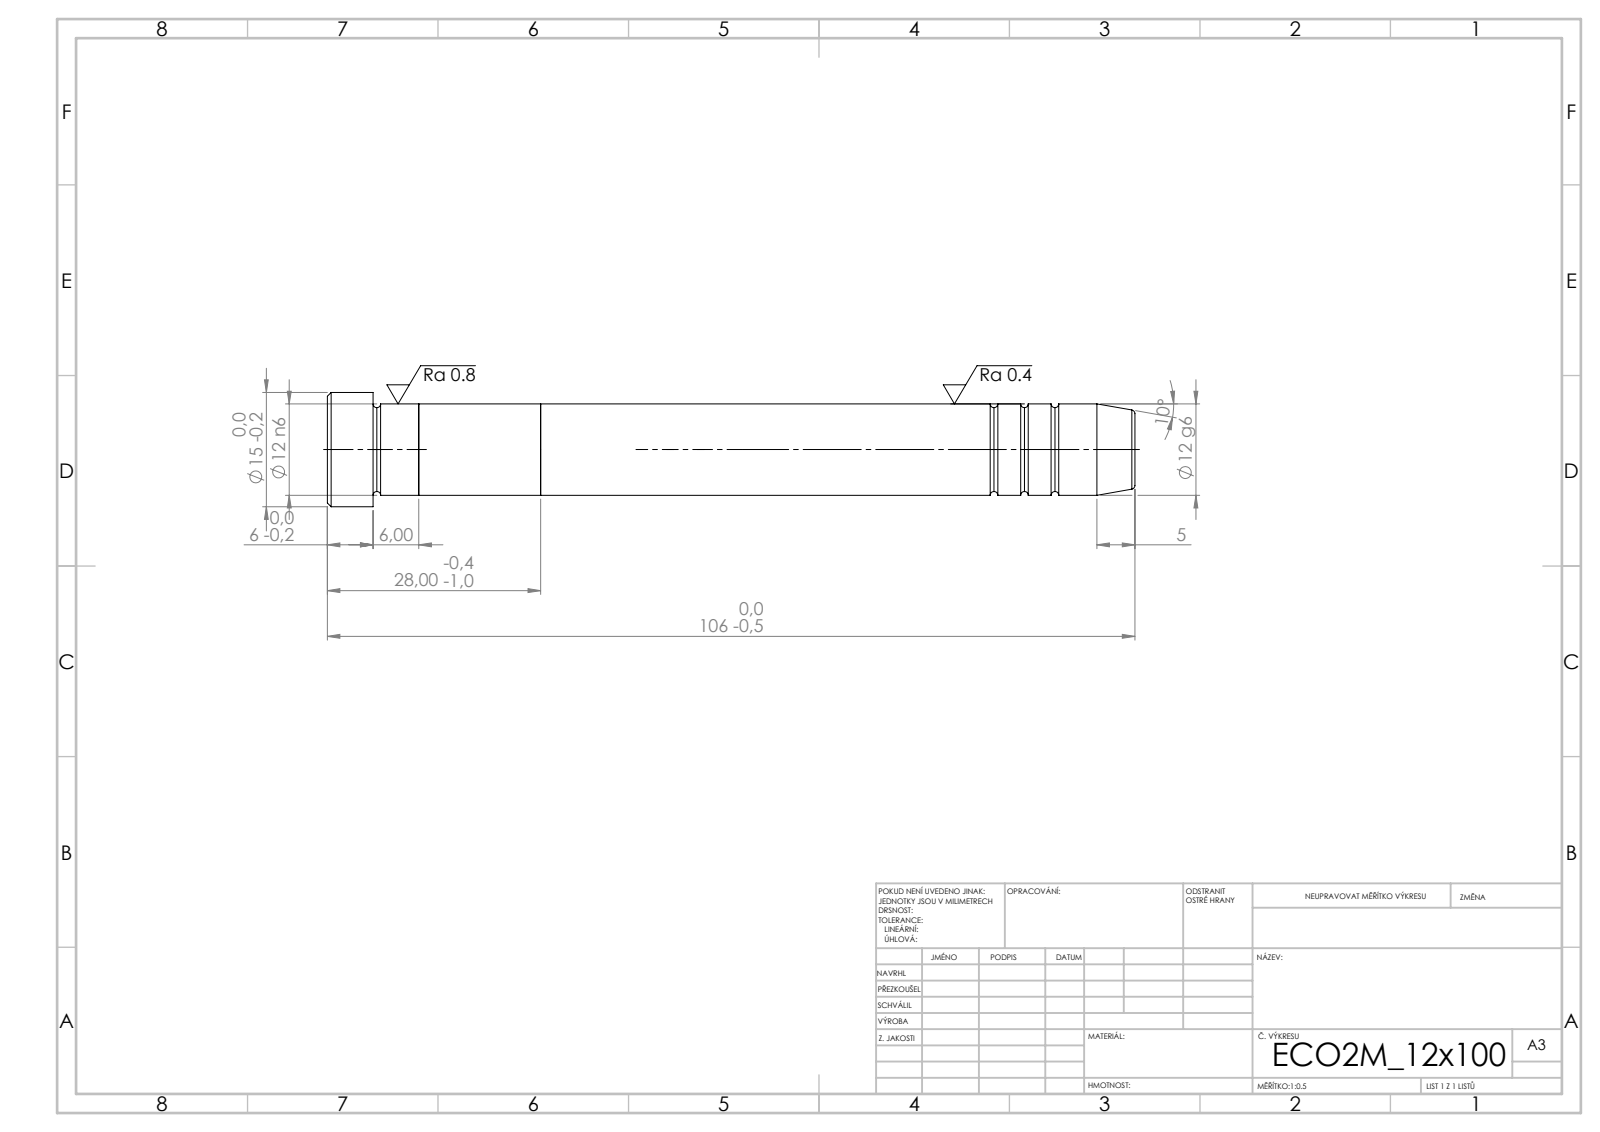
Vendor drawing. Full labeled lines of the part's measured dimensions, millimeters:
STEP written by: SolidWorks 2019 (CONFIG_CONTROL_DESIGN)
Units: millimetres
Bodies: 3 solids, 43 faces (7 planar, 14 cylindrical, 22 other)
Overall size (bounding box): 106 × 15 × 15
Volume: 12 227 mm³ · Surface area: 4 871 mm²
Round bosses / shafts (diameter × count): ⌀15 ×1, ⌀12 ×1
Main face-to-face distances: 16, 28, 12, 6, 78, 94, 106, 100, 22
